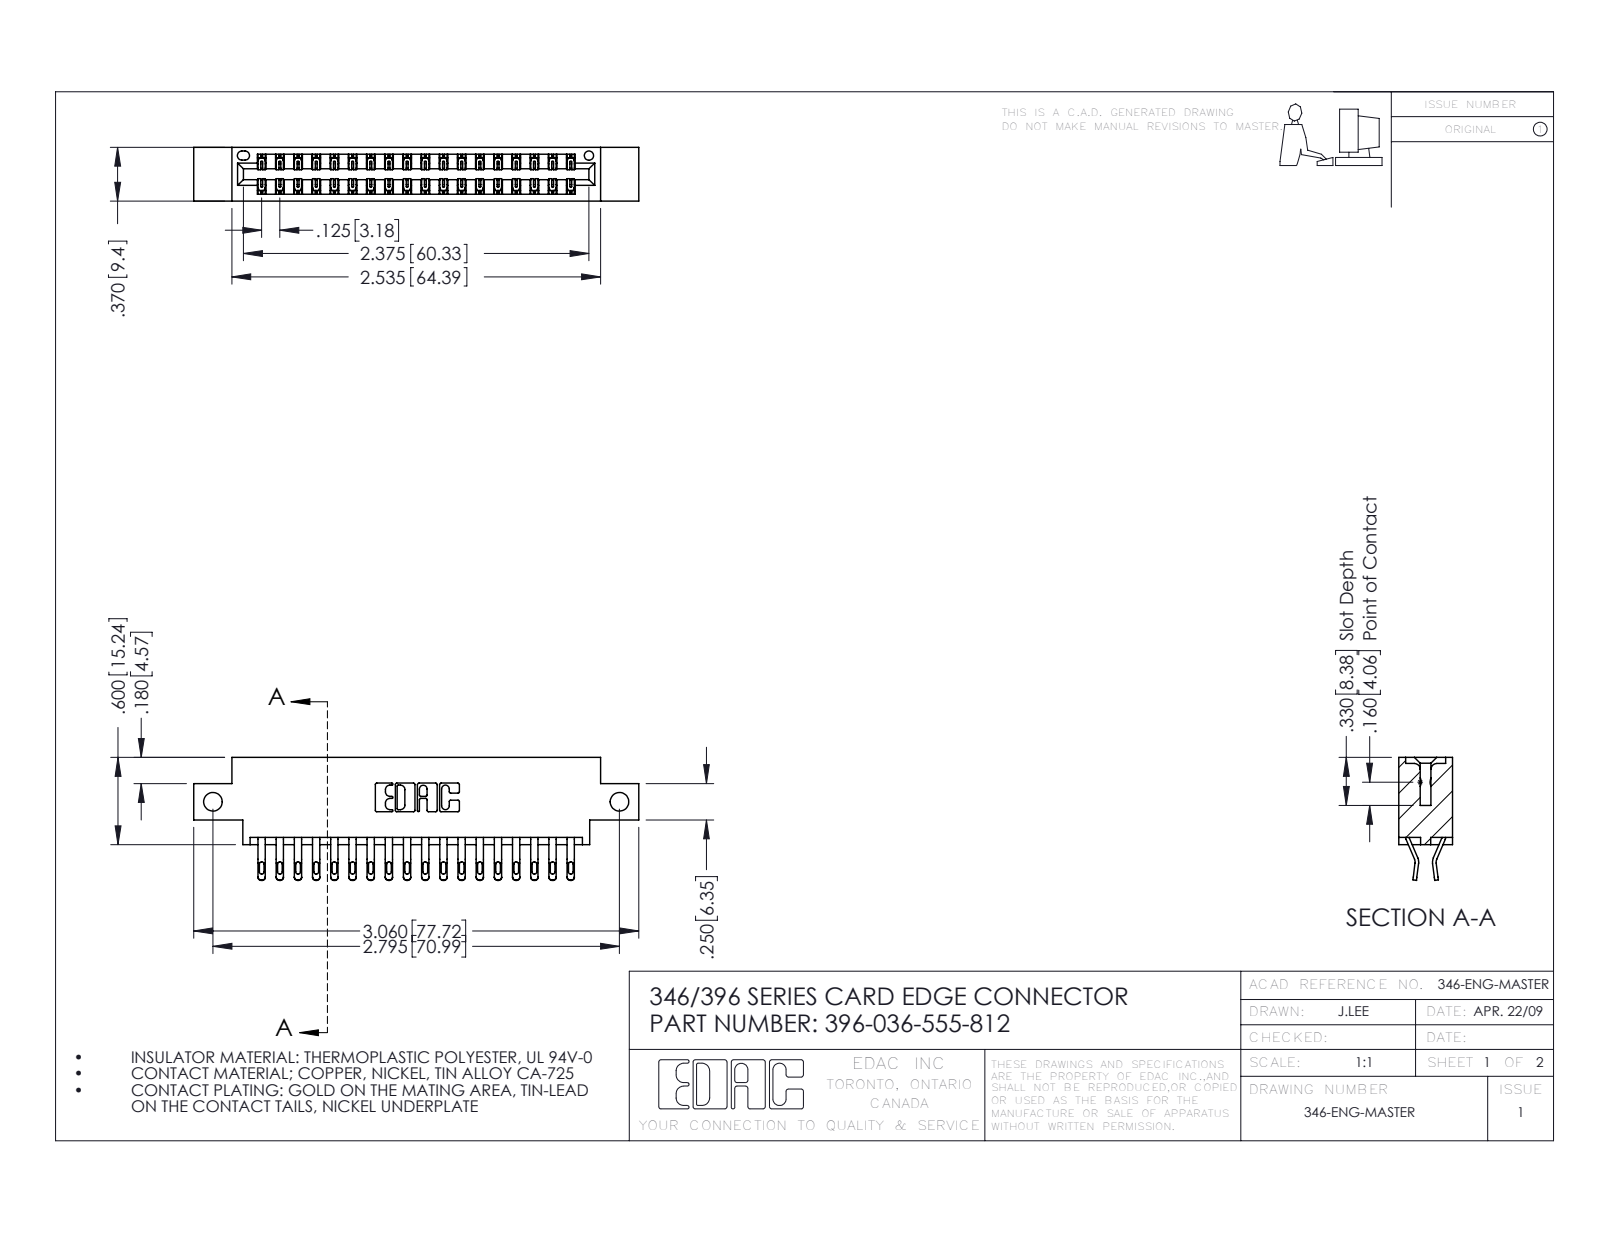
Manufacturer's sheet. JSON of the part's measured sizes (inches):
{"part_name": "346 Part_0.170 Offset - Side Mount; 396-036-555-812; 345-292-001_555 Tail", "step_written_by": "SolidWorks 2016 (CONFIG_CONTROL_DESIGN)", "units": "inches", "bodies": {"solids": 37, "faces": 2214, "planar": 1268, "cylindrical": 946, "other": 0}, "overall_size": [3.06, 0.845, 0.37], "volume_in3": 0.443, "surface_area_in2": 15.52, "round_holes": [[0.128, 2], [0.064, 1]], "partial_cylinders_radius": [[0.016, 72], [0.02, 72], [0.006, 54], [0.01, 22], [0.007, 6], [0.031, 6], [0.026, 3], [0.01, 2]], "face_to_face_distances": [0.048, 0.322, 0.37, 0.25, 0.025, 0.072, 0.298, 0.275, 0.148, 0.222], "hole_center_spacings": [2.795]}
